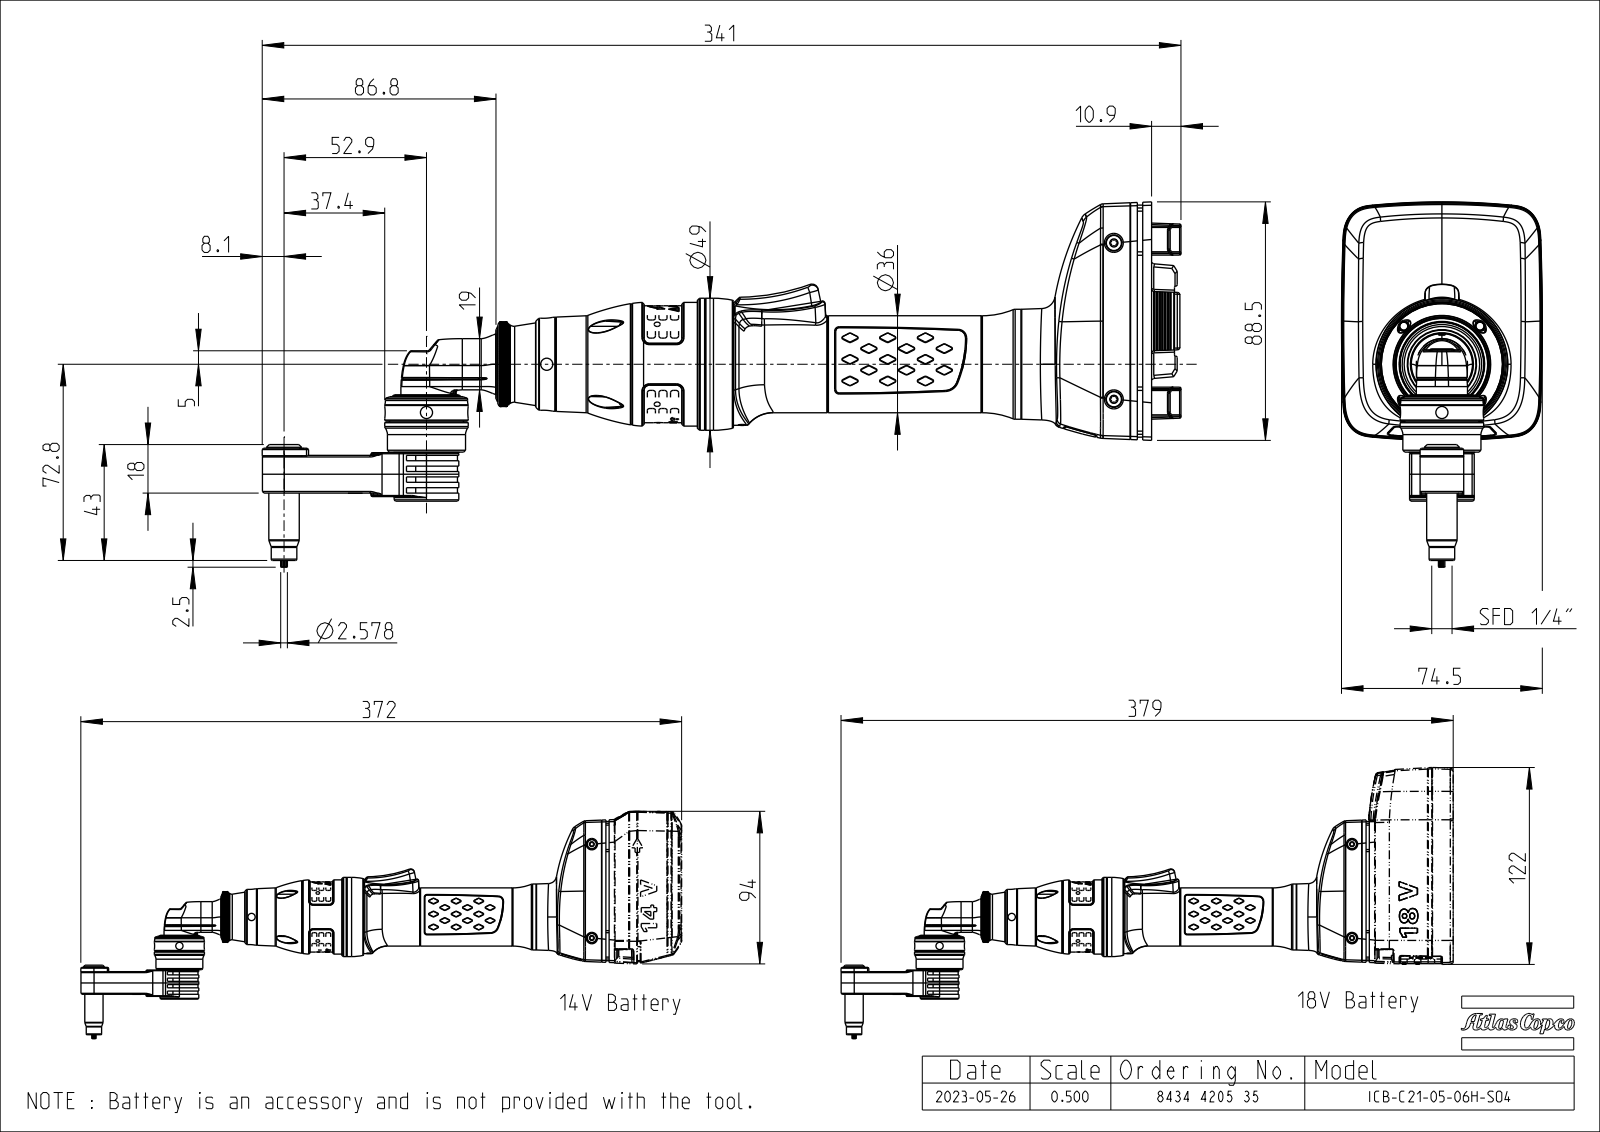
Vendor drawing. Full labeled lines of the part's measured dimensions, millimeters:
Part name (STEP PRODUCT): EXT_COMP_SW0002
STEP written by: CREO PARAMETRIC BY PTC INC, 2022414 (CONFIG_CONTROL_DESIGN)
Units: millimetres
Bodies: 2 solids, 10140 faces (6653 planar, 1197 cylindrical, 2290 other)
Overall size (bounding box): 341.1 × 135.6 × 74.5
Volume: 467 000 mm³ · Surface area: 84 640 mm²
Round holes (diameter × count): ⌀2 ×4, ⌀2.1 ×4, ⌀4.5 ×4, ⌀2.6 ×2, ⌀3.6 ×2, ⌀3.7 ×2, ⌀6 ×2, ⌀2.5 ×1, ⌀2.9 ×1, ⌀3.5 ×1, ⌀4.1 ×1, ⌀5 ×1
Round bosses / shafts (diameter × count): ⌀8 ×4, ⌀5.6 ×3, ⌀3.5 ×2, ⌀49 ×1, ⌀47.4 ×1, ⌀45.9 ×1, ⌀45.3 ×1, ⌀43.5 ×1
Partial cylindrical surfaces — rounded edges, fillets, slot ends (radius × count): R0.5 ×74, R1 ×74, R0.3 ×38, R0.2 ×34, R0.3 ×30, R0.5 ×30, R0.2 ×24, R0.4 ×24
Main face-to-face distances: 168.7, 3, 120.5, 48.2, 120.5, 48.2, 22.5, 191.1, 70.6, 70.6
Hole centre spacings: 5.5, 7.8, 12, 4, 8.8, 8.8, 9.7, 10
